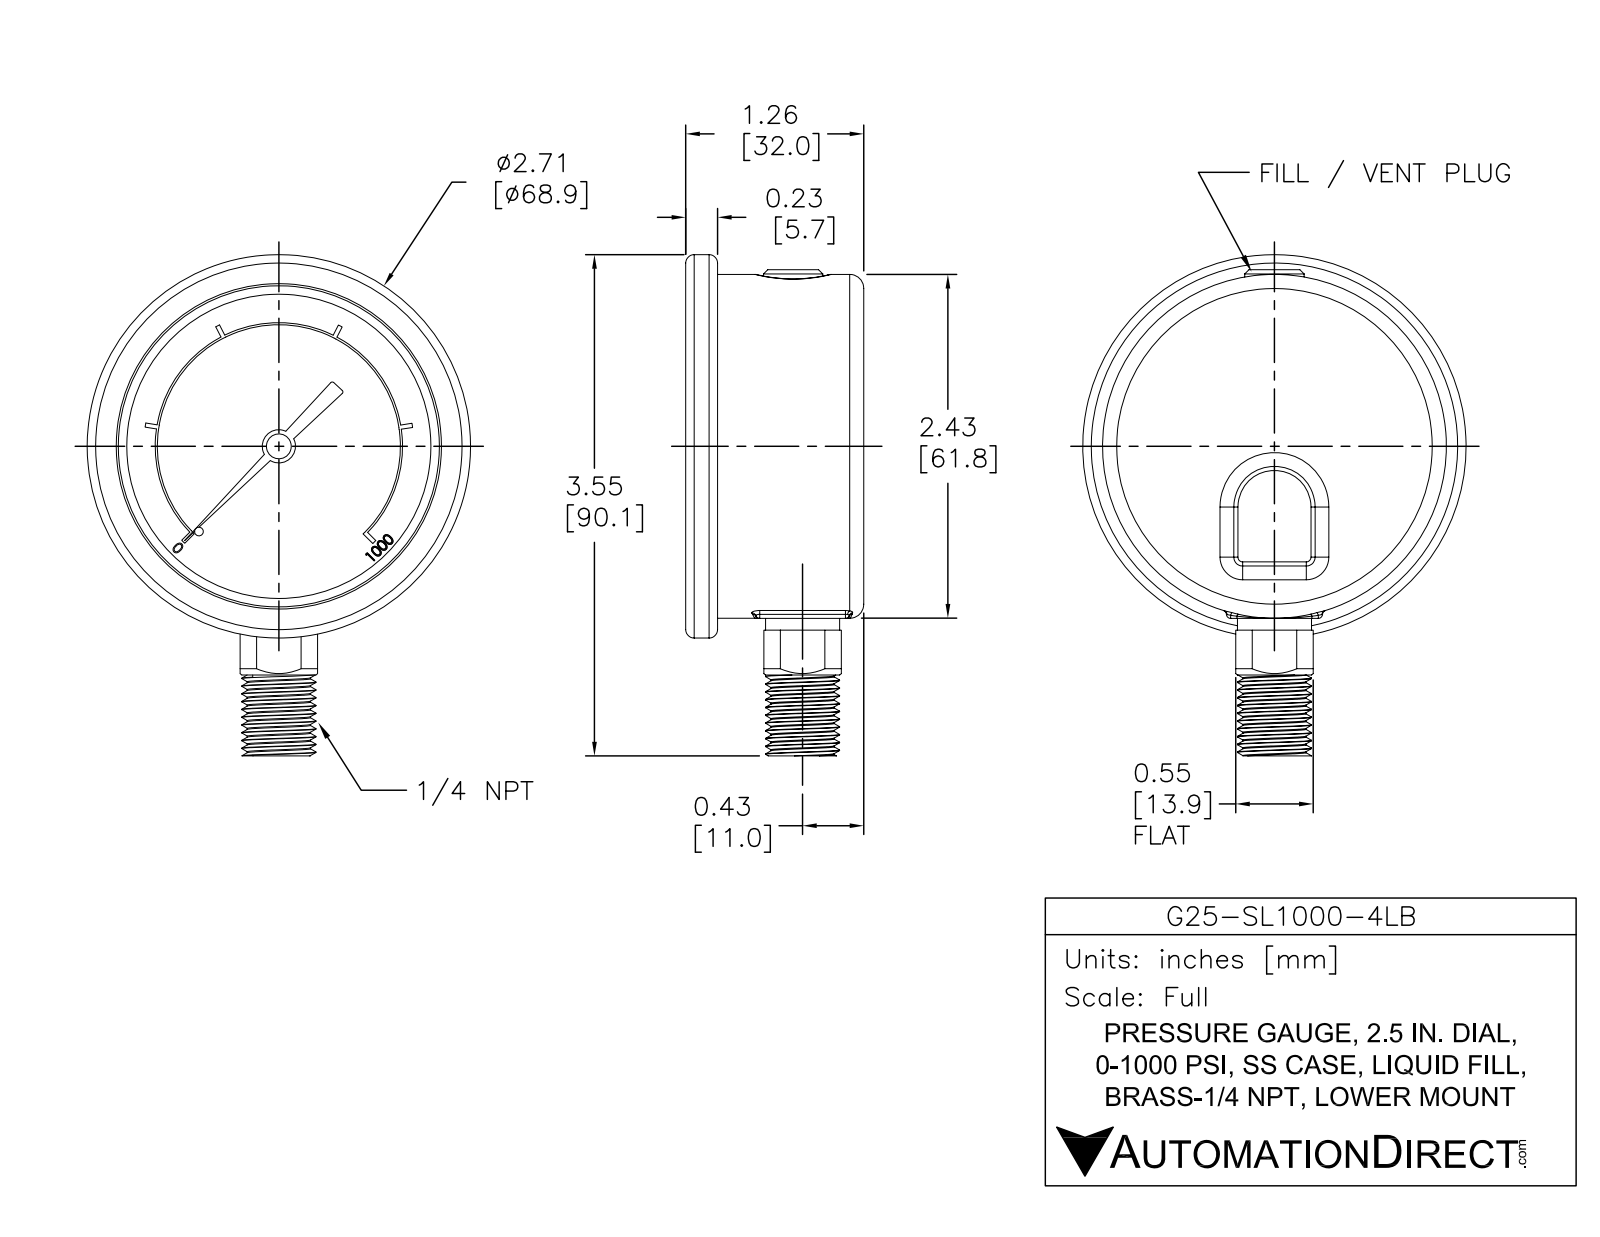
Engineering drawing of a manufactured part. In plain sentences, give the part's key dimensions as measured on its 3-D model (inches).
The part is named "G25-SL1000-4LB". Its 3-D file was written by "SolidWorks 2021 (AUTOMOTIVE_DESIGN)". It is 1 solid with 354 faces: 197 planar, 85 cylindrical and 72 other. Overall it measures 3.546 by 2.713 by 1.26 inches. Its volume is 5.273 cubic inches and its surface area 24.68 square inches. Round holes: 1 of diameter 0.027, 1 of diameter 0.071, 1 of diameter 0.119, 1 of diameter 2.272. Round bosses or shafts: 1 of diameter 2.713, 1 of diameter 2.433, 1 of diameter 0.524, 1 of diameter 0.42, 1 of diameter 0.235, 1 of diameter 0.176, 1 of diameter 0.14, 1 of diameter 0.041. Partial cylindrical surfaces (rounded edges, fillets, slot ends): 9 of radius 0.03, 3 of radius 0.1, 2 of radius 0.015, 1 of radius 0.316, 1 of radius 0.86, 1 of radius 0.875. The main face-to-face distances are 1.01, 1.26, 0.25, 1.035, 0.025, 0.225, 0.1, 0.91, 0.935, 1.16. The hole center spacings are 0.067.
